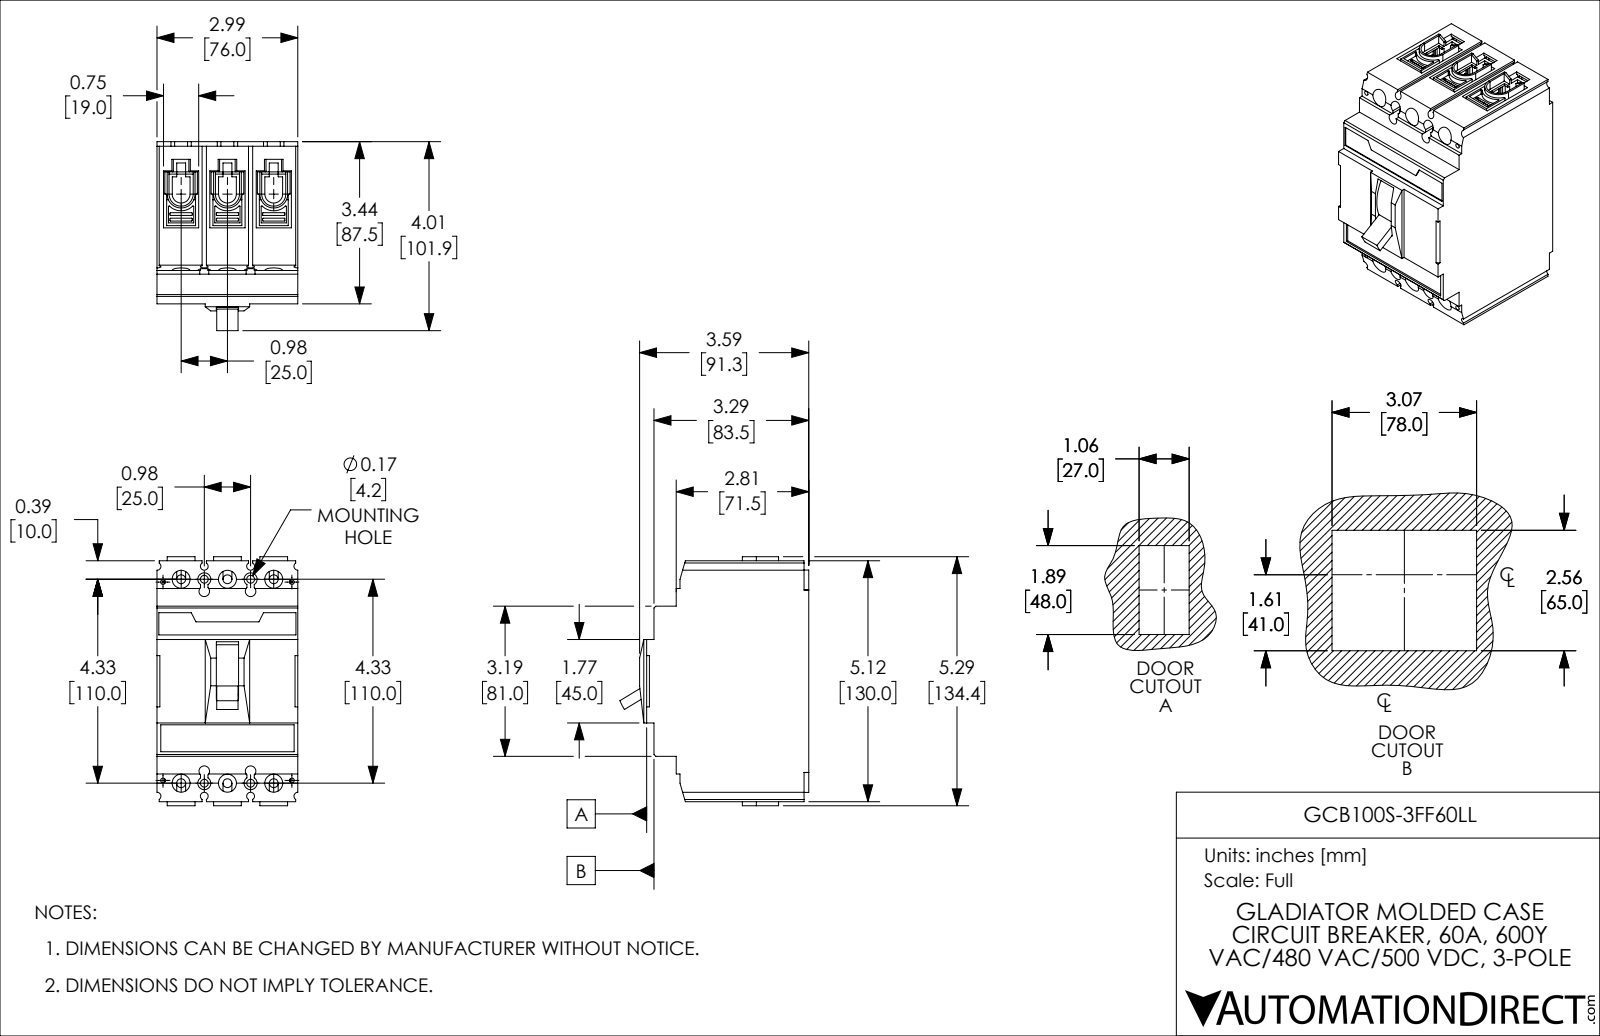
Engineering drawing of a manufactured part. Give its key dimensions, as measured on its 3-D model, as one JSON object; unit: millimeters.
{"part_name": "GCB100S-3FF60LL", "step_written_by": "SolidWorks 2021 (CONFIG_CONTROL_DESIGN)", "units": "millimeters", "bodies": {"solids": 1, "faces": 1256, "planar": 784, "cylindrical": 424, "other": 48}, "overall_size": [134.4, 101.9, 76], "volume_mm3": 708400, "surface_area_mm2": 95810, "round_holes": [[4.2, 8], [4.8, 6], [9.7, 6], [2.5, 4], [7, 4]], "partial_cylinders_radius": [[0.3, 86], [0.5, 38], [1, 14], [4, 14], [0.6, 6], [2.1, 4], [2.8, 4], [4.8, 3]], "face_to_face_distances": [76, 25, 15.8, 114.2, 44, 2.8, 87.5, 19, 50, 130], "hole_center_spacings": [12.5, 14.3, 25, 110.7, 117.7, 112.8, 110, 7]}
